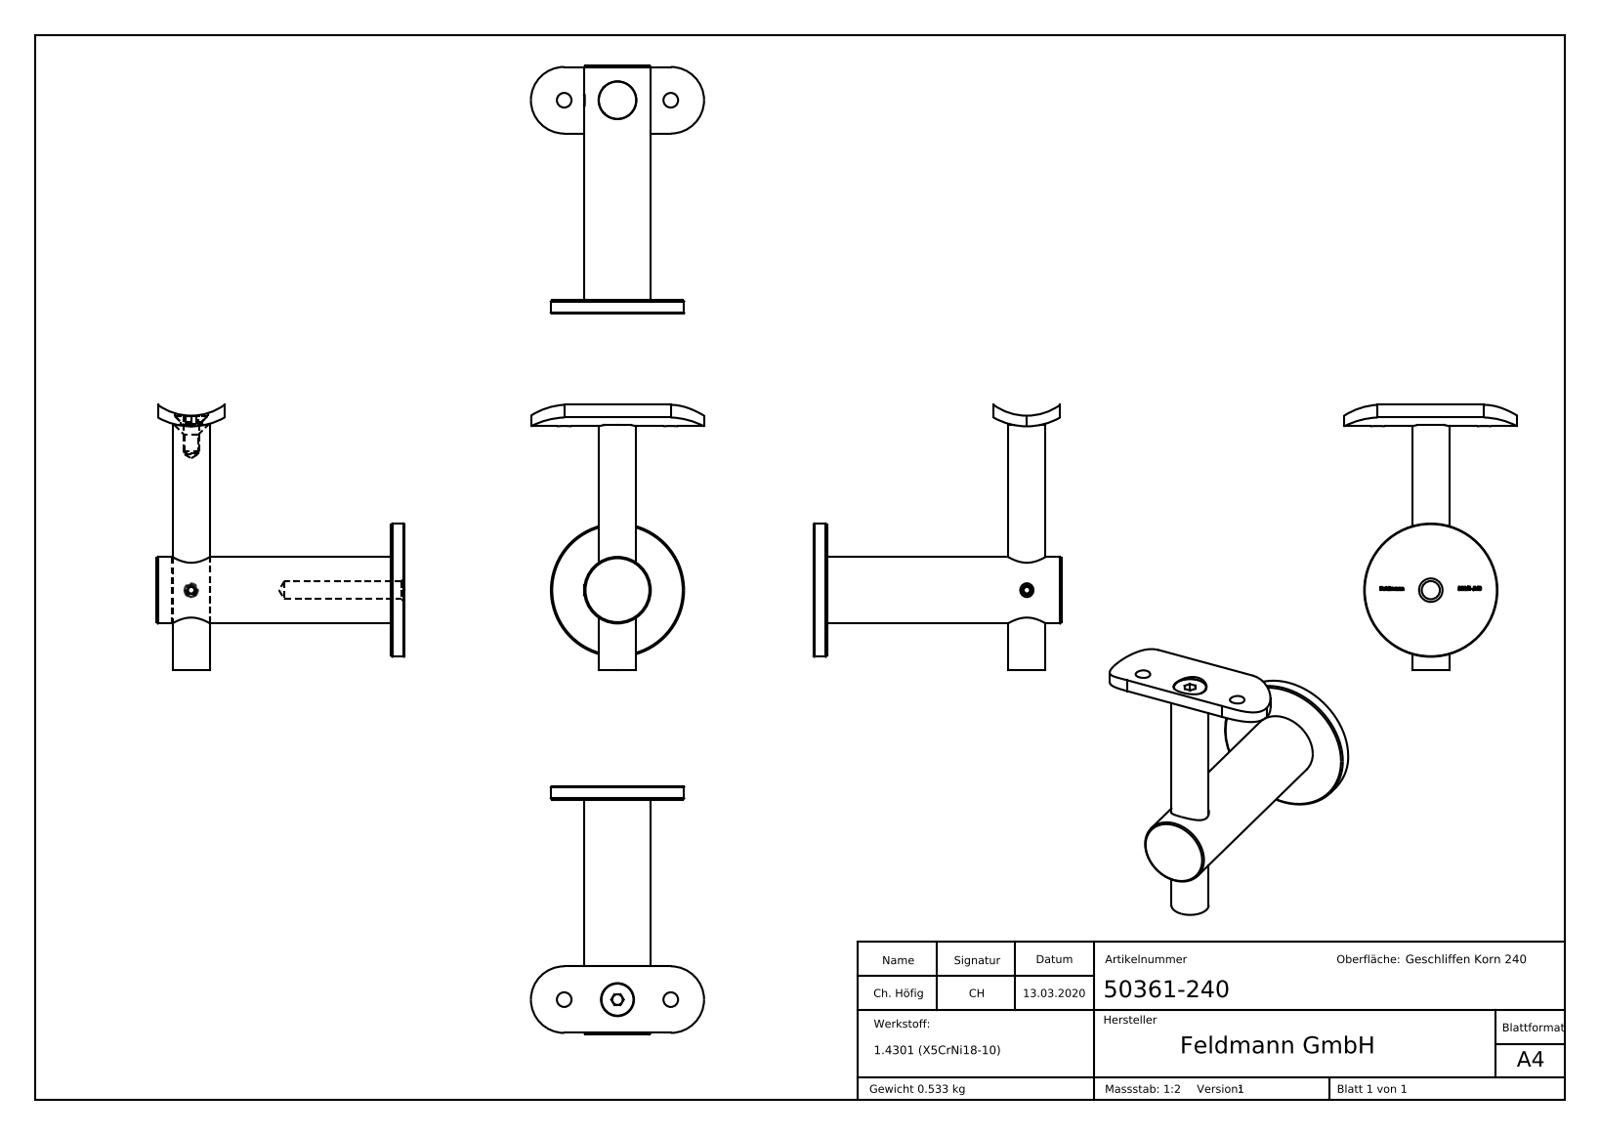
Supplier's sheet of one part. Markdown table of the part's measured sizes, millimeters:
| quantity | value |
| --- | --- |
| part name | DIN913_DIN 913 M5x5; 50361-240; 503XX-240 Teil3_50361-240 Teil3; DIN-7991 M3-M10 (+7 more) |
| STEP written by | SolidWorks 2015 (CONFIG_CONTROL_DESIGN) |
| units | millimeters |
| bodies | 5 solids, 295 faces (155 planar, 22 cylindrical, 118 other) |
| overall size | 99.58 × 93 × 88 |
| volume | 67 517 mm³ |
| surface area | 22 274 mm² |
| round holes (diameter × count) | 5.5 × 2, 4.2 × 1, 5 × 1, 6.8 × 1, 8.1 × 1, 12.4 × 1, 14.2 × 1 |
| round bosses / shafts (diameter × count) | 50 × 1, 25 × 1, 14 × 1, 12 × 1, 6 × 1, 5 × 1 |
| partial cylindrical surfaces (radius × count) | 12.5 × 2, 21.2 × 1, 25.2 × 1 |
| main face-to-face distances | 5, 93, 88, 0.5, 92.5, 62.5, 87.5, 67.5, 25, 25.5 |
| hole center spacings | 20, 40 |
